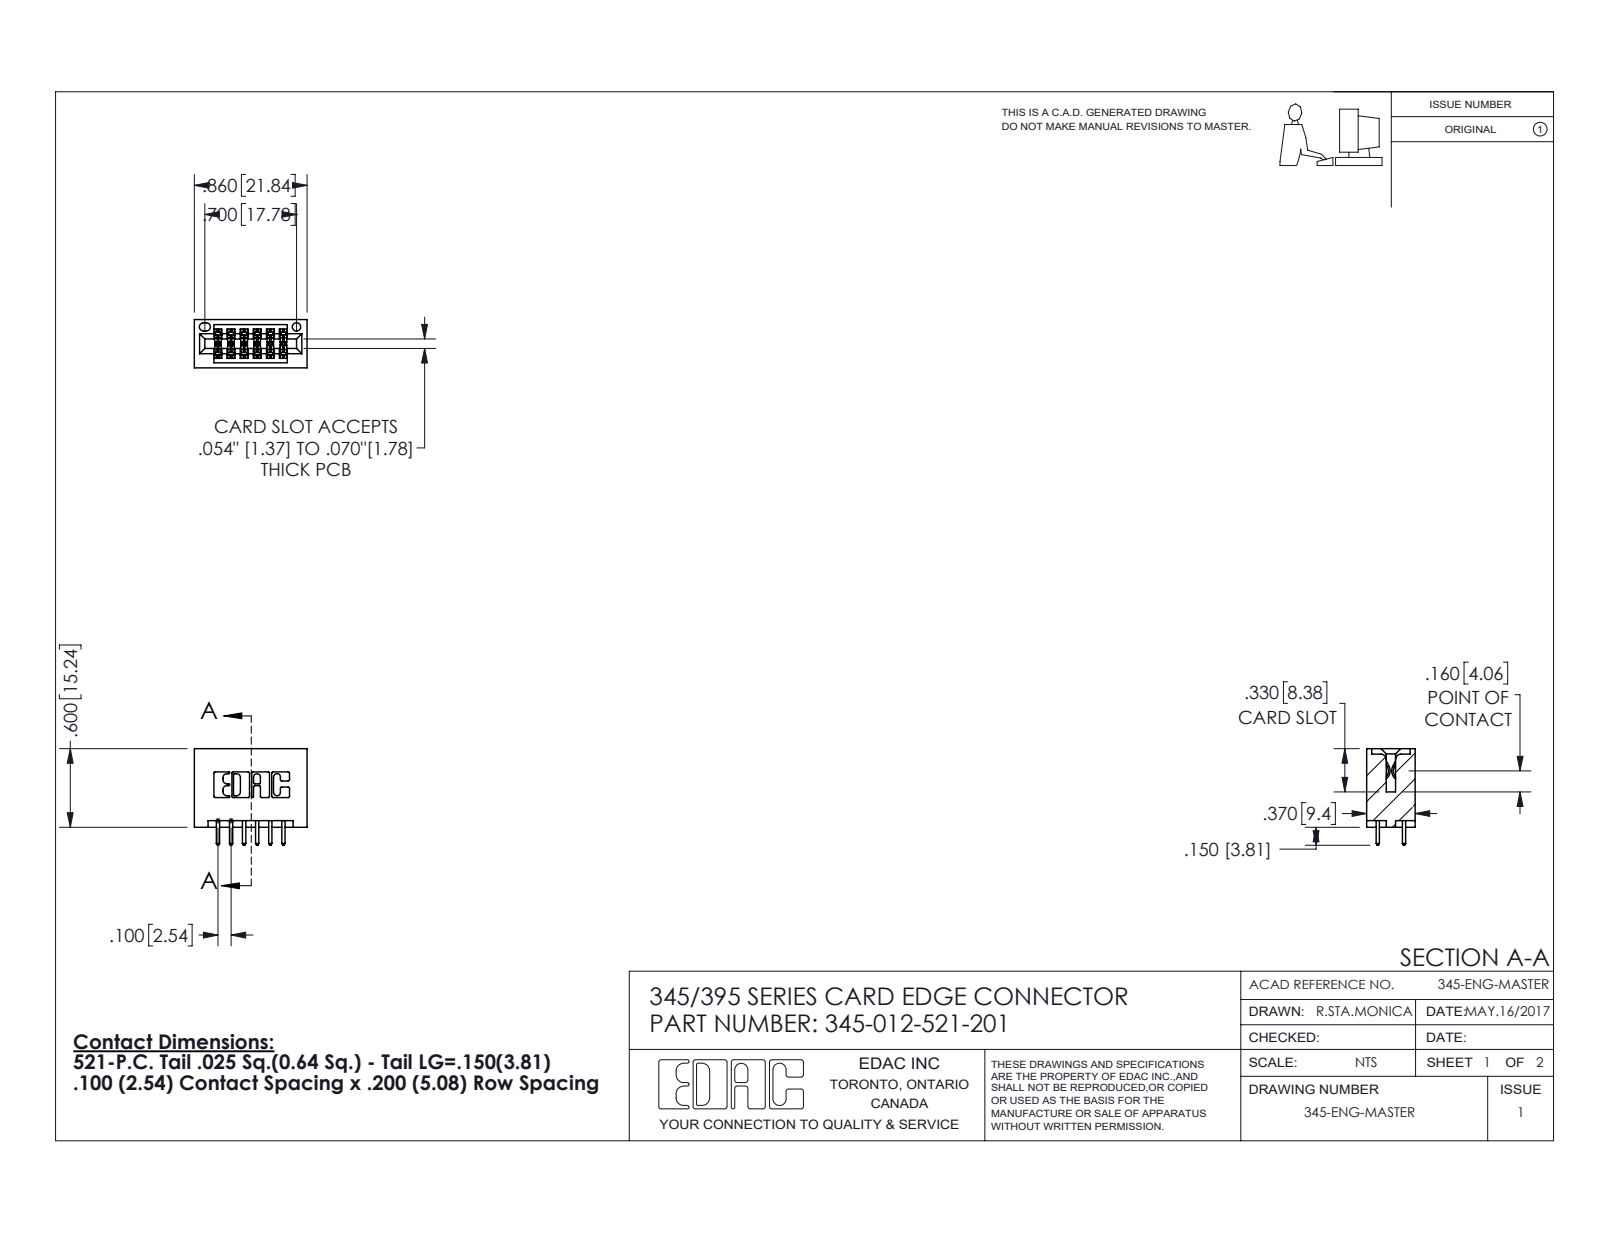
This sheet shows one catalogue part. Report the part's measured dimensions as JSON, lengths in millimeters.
{"part_name": "345-012-521-201; 345 Part_No Mounting Lugs; 345-292-001_345-293-121", "step_written_by": "SolidWorks 2016 (CONFIG_CONTROL_DESIGN)", "units": "millimeters", "bodies": {"solids": 13, "faces": 718, "planar": 472, "cylindrical": 246, "other": 0}, "overall_size": [21.8, 18.7, 9.4], "volume_mm3": 2390, "surface_area_mm2": 3120, "round_holes": [[1.6, 1]], "partial_cylinders_radius": [[0.3, 22], [0.2, 18], [0.3, 12], [0.2, 6], [0.8, 6], [0.7, 3], [0.4, 2], [0.5, 2]], "face_to_face_distances": [5.1, 7.6, 1.8, 2.5, 9.4, 2.5, 6.9, 0.6, 7.6, 5.7]}
